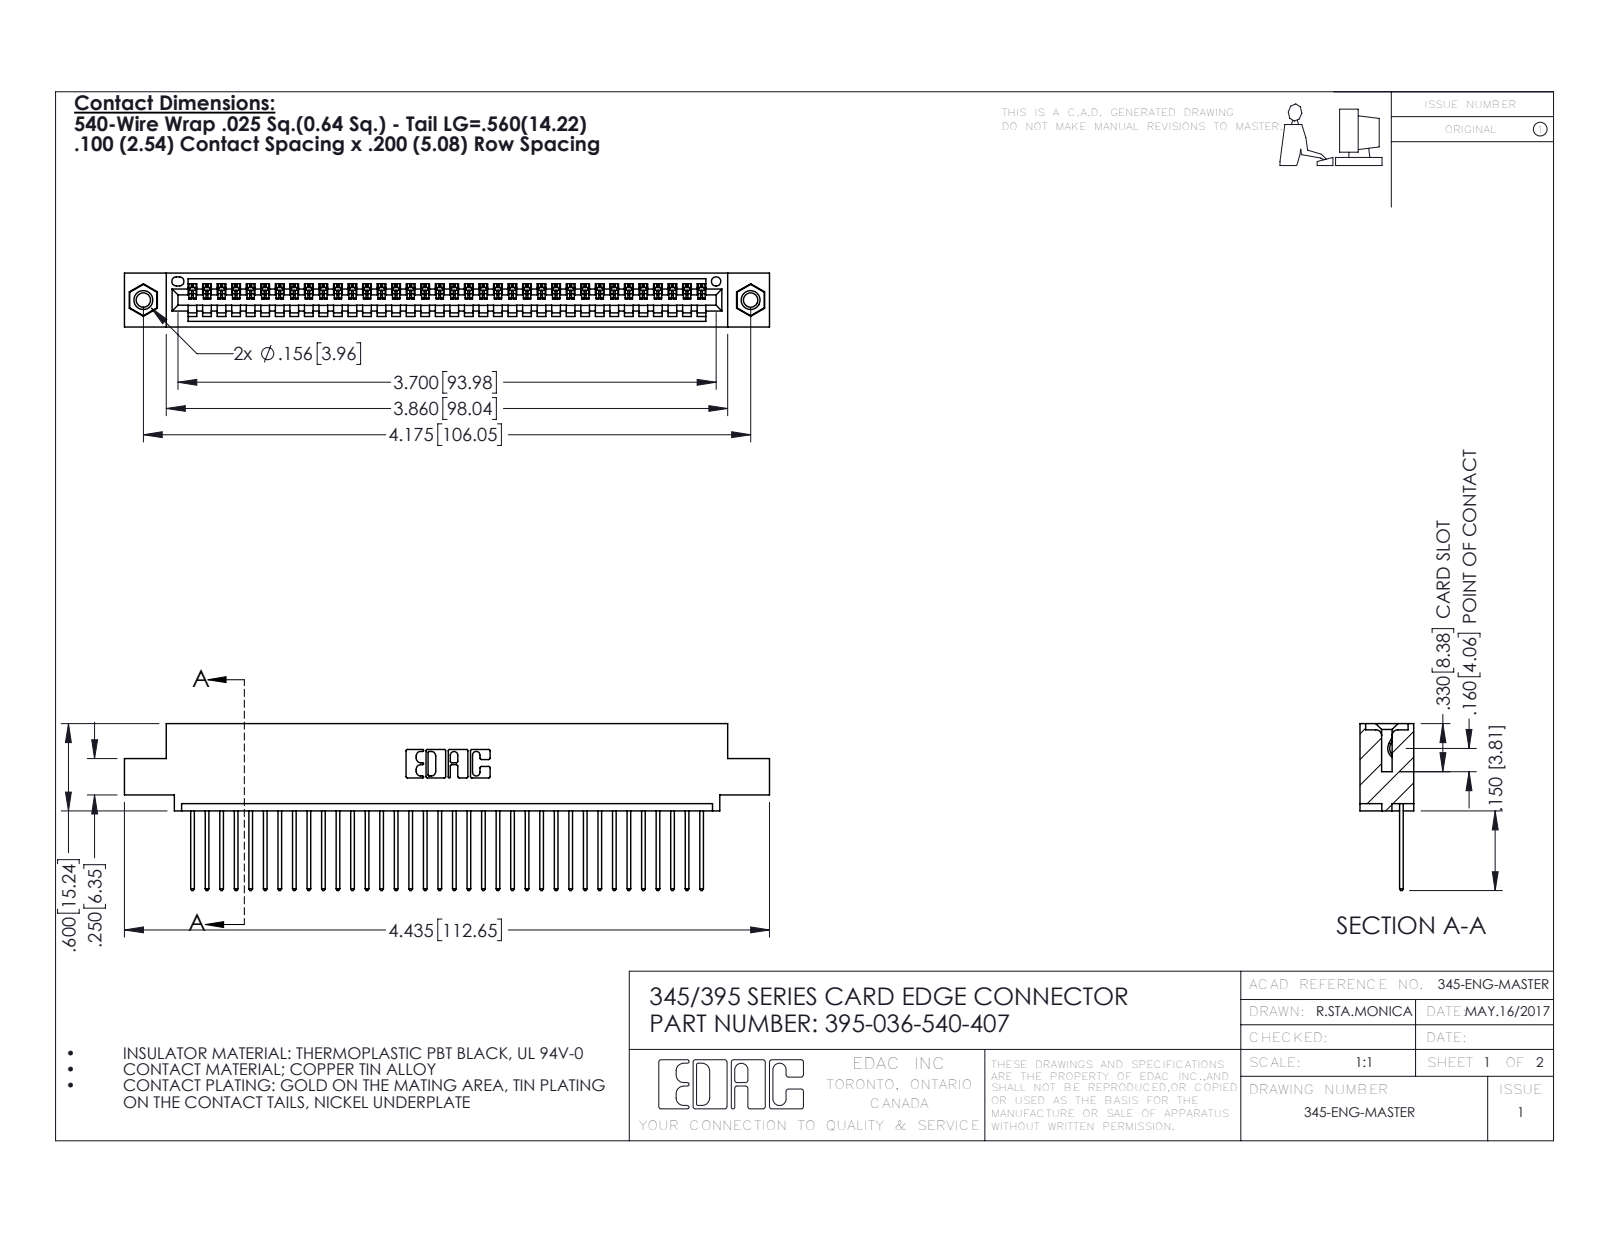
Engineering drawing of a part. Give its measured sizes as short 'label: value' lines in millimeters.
name: 345-250-001_345-250-005-103; 395-036-540-407; 345-292-001_345-293-140; 345 Part_0.110 Offset - 0.156 Dia-TI
written by: SolidWorks 2016 (CONFIG_CONTROL_DESIGN)
unit: mm
bodies: 39 solids, 2278 faces (1556 planar, 706 cylindrical, 16 other)
size: 112.6 × 29.1 × 9.4
volume: 10 600 mm³; area: 14 480 mm²
holes: 2× ⌀2.5, 2× ⌀3.2, 2× ⌀4, 1× ⌀1.6
bosses: 2× ⌀3.9
rounds: 72× R0.2, 72× R0.3, 22× R0.3, 6× R0.2, 6× R0.8, 3× R0.7, 2× R0.8, 2× R1
face distances: 1.8, 7.6, 9.4, 2.5, 6.9, 0.6, 5.1, 5.7, 3.8, 1.8
hole spacings: 6.9, 100.1, 106
